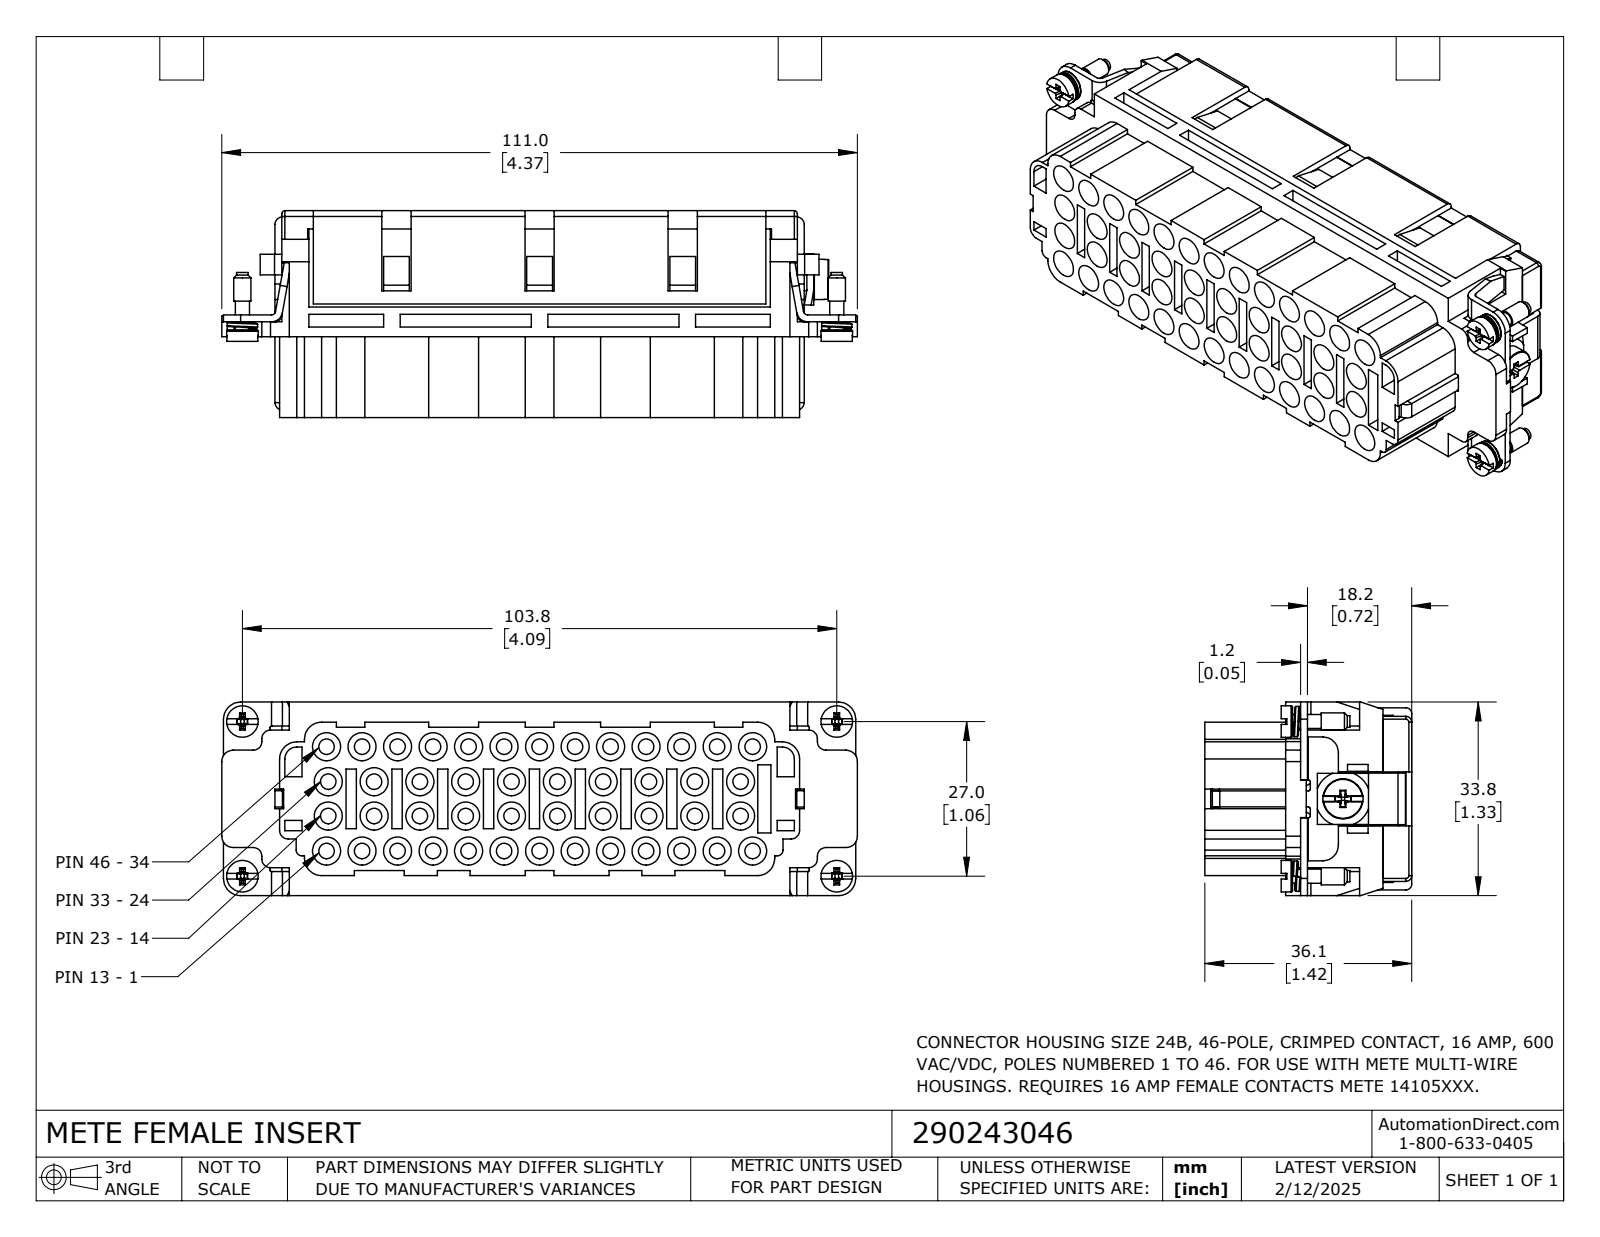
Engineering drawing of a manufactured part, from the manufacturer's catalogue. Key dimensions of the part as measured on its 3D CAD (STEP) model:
Part name (STEP PRODUCT): 290243046
STEP written by: SolidWorks 2024 (CONFIG_CONTROL_DESIGN)
Units: inches
Bodies: 13 solids, 2435 faces (1214 planar, 915 cylindrical, 306 other)
Overall size (bounding box): 4.37 × 1.421 × 1.331
Volume: 3.517 in³ · Surface area: 107.3 in²
Round holes (diameter × count): ⌀0.106 ×49, ⌀0.189 ×46, ⌀0.193 ×46, ⌀0.071 ×18, ⌀0.114 ×4, ⌀0.13 ×1
Round bosses / shafts (diameter × count): ⌀0.063 ×18, ⌀0.217 ×4, ⌀0.209 ×4, ⌀0.118 ×4, ⌀0.096 ×4, ⌀0.079 ×4, ⌀0.091 ×3, ⌀0.276 ×1
Partial cylindrical surfaces — rounded edges, fillets, slot ends (radius × count): R0.059 ×56, R0.118 ×56, R0.165 ×46, R0.01 ×32, R0.004 ×12, R0.012 ×12, R0.051 ×10, R0.02 ×8
Main face-to-face distances: 0.055, 0.051, 1.197, 0.047, 0.035, 0.134, 0.027, 1.201, 1.146, 0.126
Hole centre spacings: 0.315, 0.394, 0.63, 0.673, 0.945, 0.974, 1.26, 1.282
